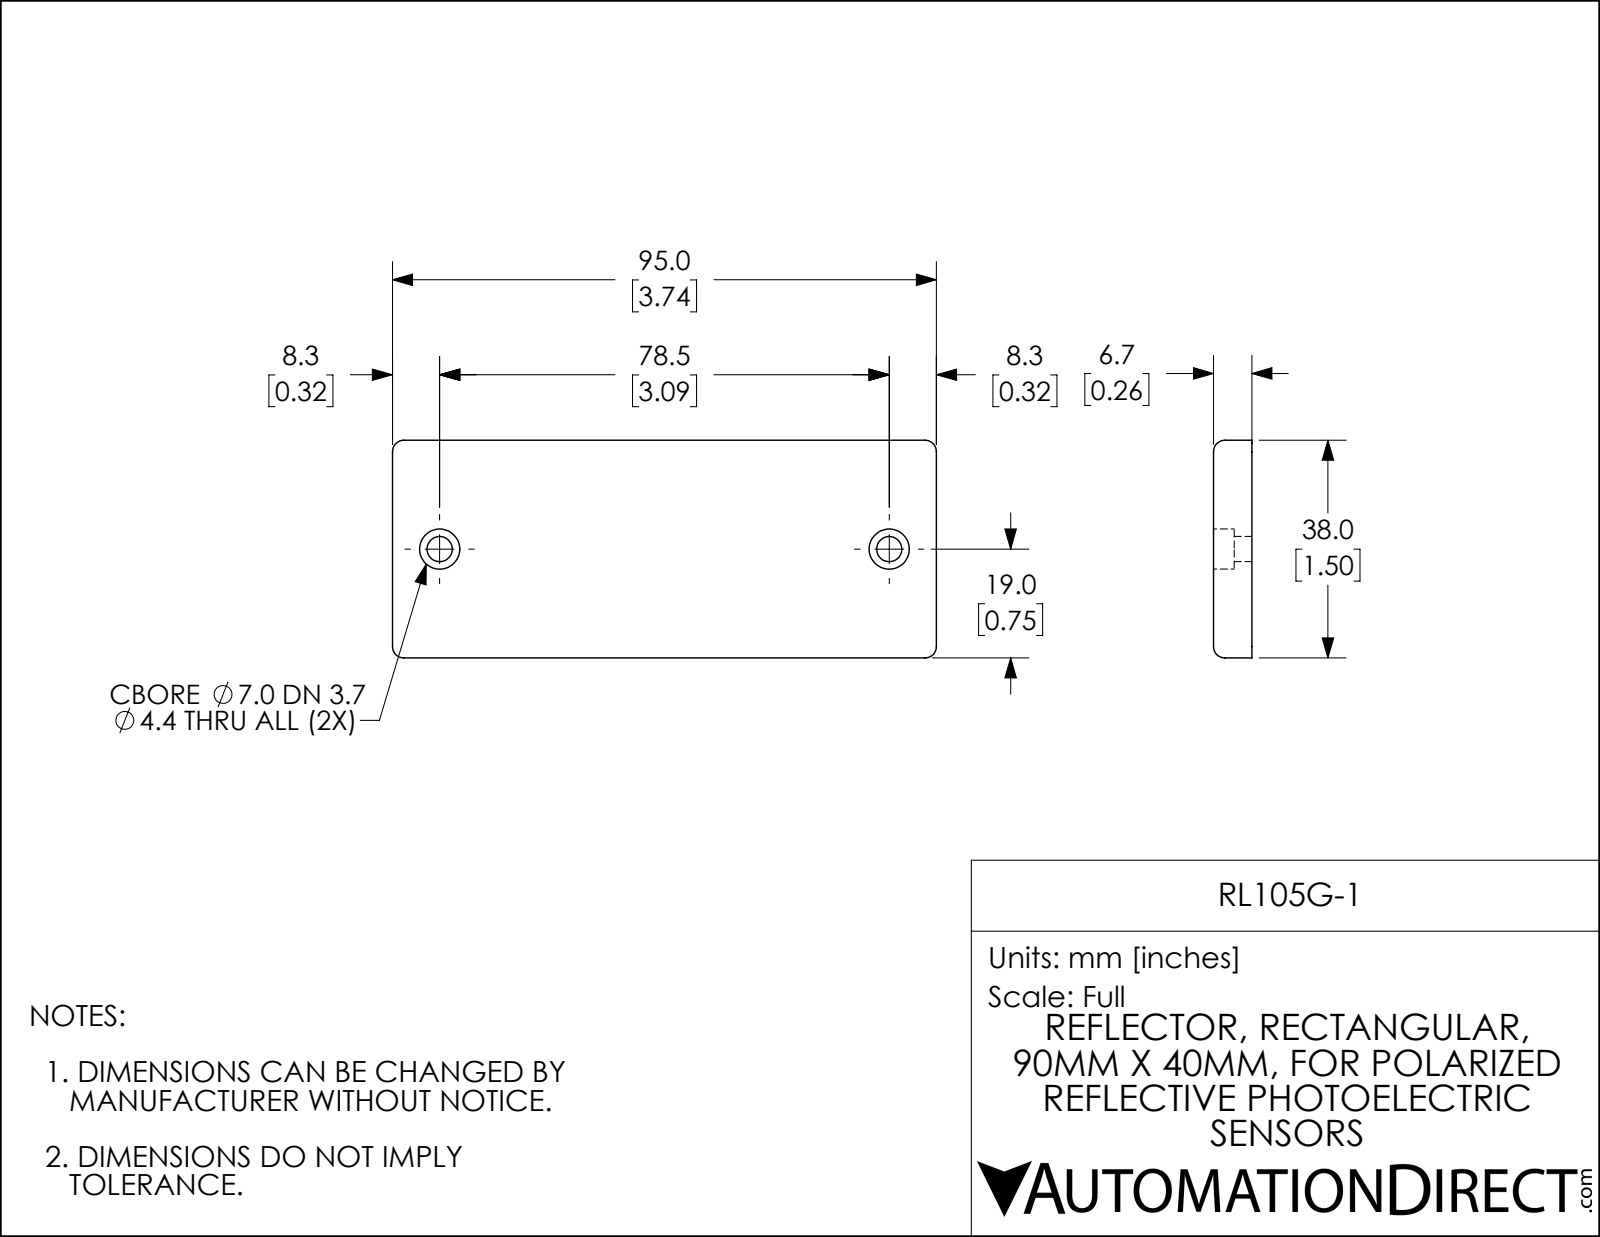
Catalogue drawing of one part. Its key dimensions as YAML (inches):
part_name: "RL105G-1"
step_written_by: "SolidWorks 2017 (AUTOMOTIVE_DESIGN)"
units: inches
bodies: {solids: 1, faces: 24, planar: 8, cylindrical: 12, other: 4}
overall_size: [3.74, 1.496, 0.264]
volume: 1.438
surface_area: 13.84
round_holes:
  - {diameter: 0.173, count: 2}
  - {diameter: 0.276, count: 2}
partial_cylinders:
  - {radius: 0.079, count: 8}
face_to_face_distances: [0.264, 1.496, 3.74, 0.122, 0.142]
hole_center_spacings: [3.091]
